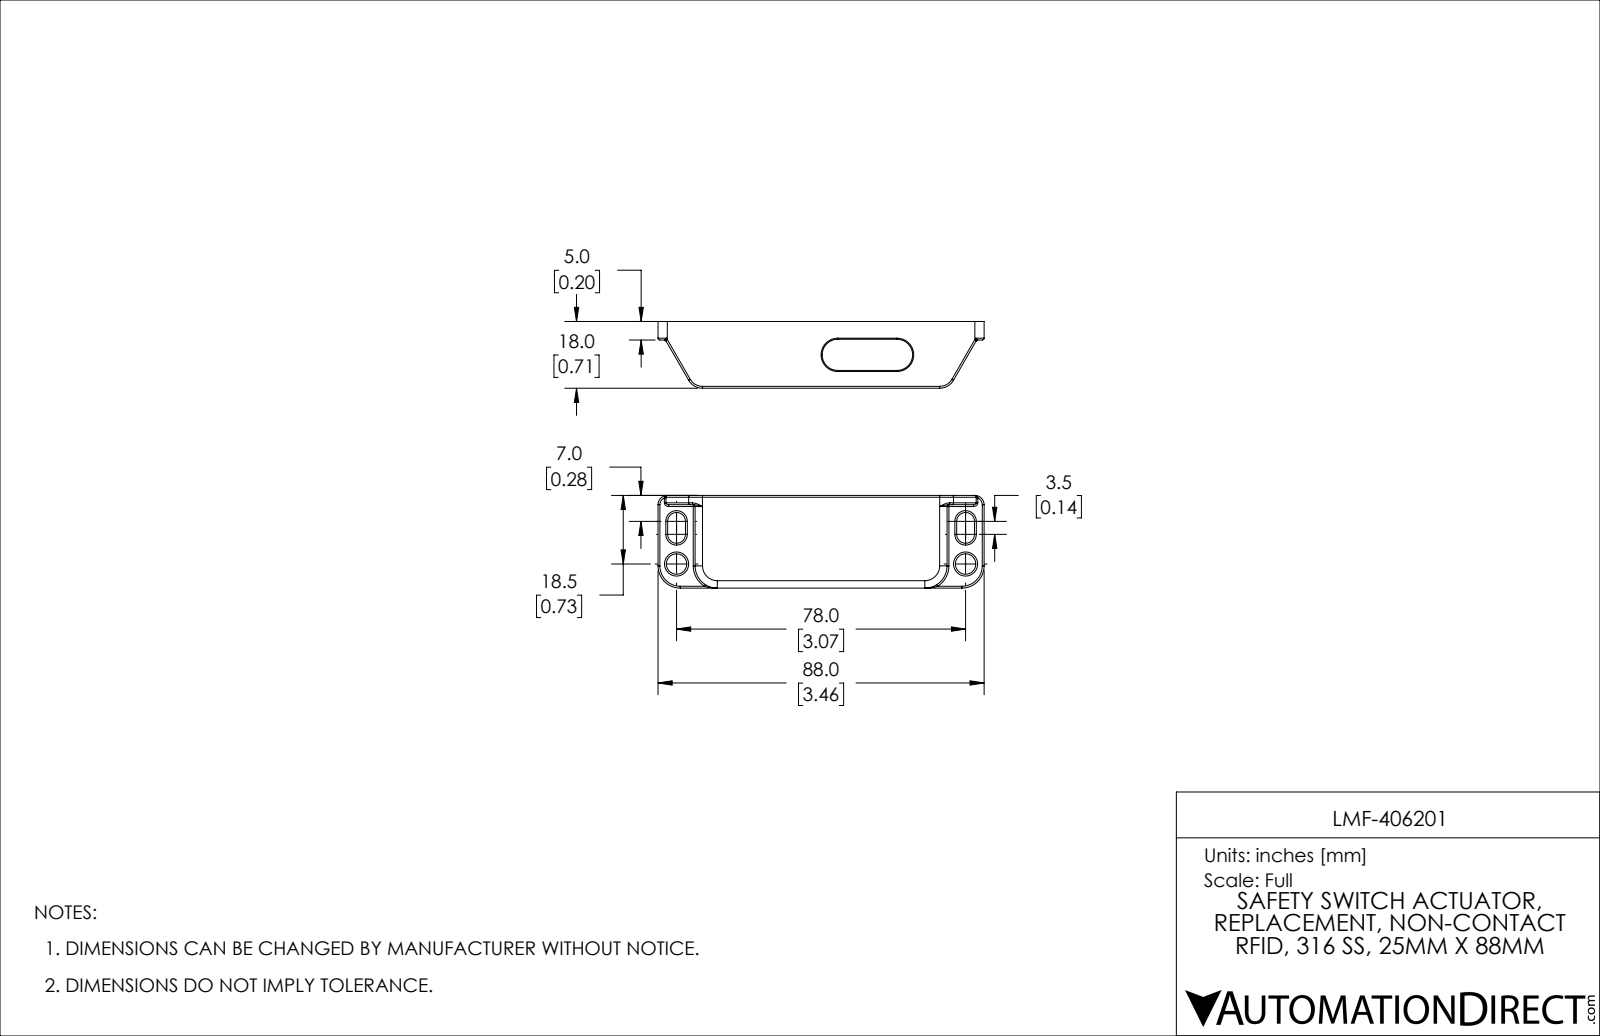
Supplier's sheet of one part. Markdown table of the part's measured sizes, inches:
| quantity | value |
| --- | --- |
| part name | LMF-406201 |
| STEP written by | SolidWorks 2019 (AUTOMOTIVE_DESIGN) |
| units | inches |
| bodies | 5 solids, 635 faces (286 planar, 150 cylindrical, 199 other) |
| overall size | 3.465 × 0.984 × 0.709 |
| volume | 0.898 in³ |
| surface area | 23.46 in² |
| round holes (diameter × count) | 0.138 × 2, 0.217 × 2, 0.24 × 2, 0.283 × 2 |
| round bosses / shafts (diameter × count) | 0.276 × 2, 0.236 × 2, 0.126 × 2 |
| partial cylindrical surfaces (radius × count) | 0.02 × 65, 0.012 × 30, 0.236 × 6, 0.094 × 4, 0.157 × 4, 0.079 × 3, 0.008 × 2, 0.098 × 2 |
| main face-to-face distances | 0.079, 0.059, 0.618, 0.697, 0.906, 0.984, 0.559, 0.638, 0.071, 0.709 |
| hole center spacings | 0.589, 2.528, 1.969, 3.071 |
